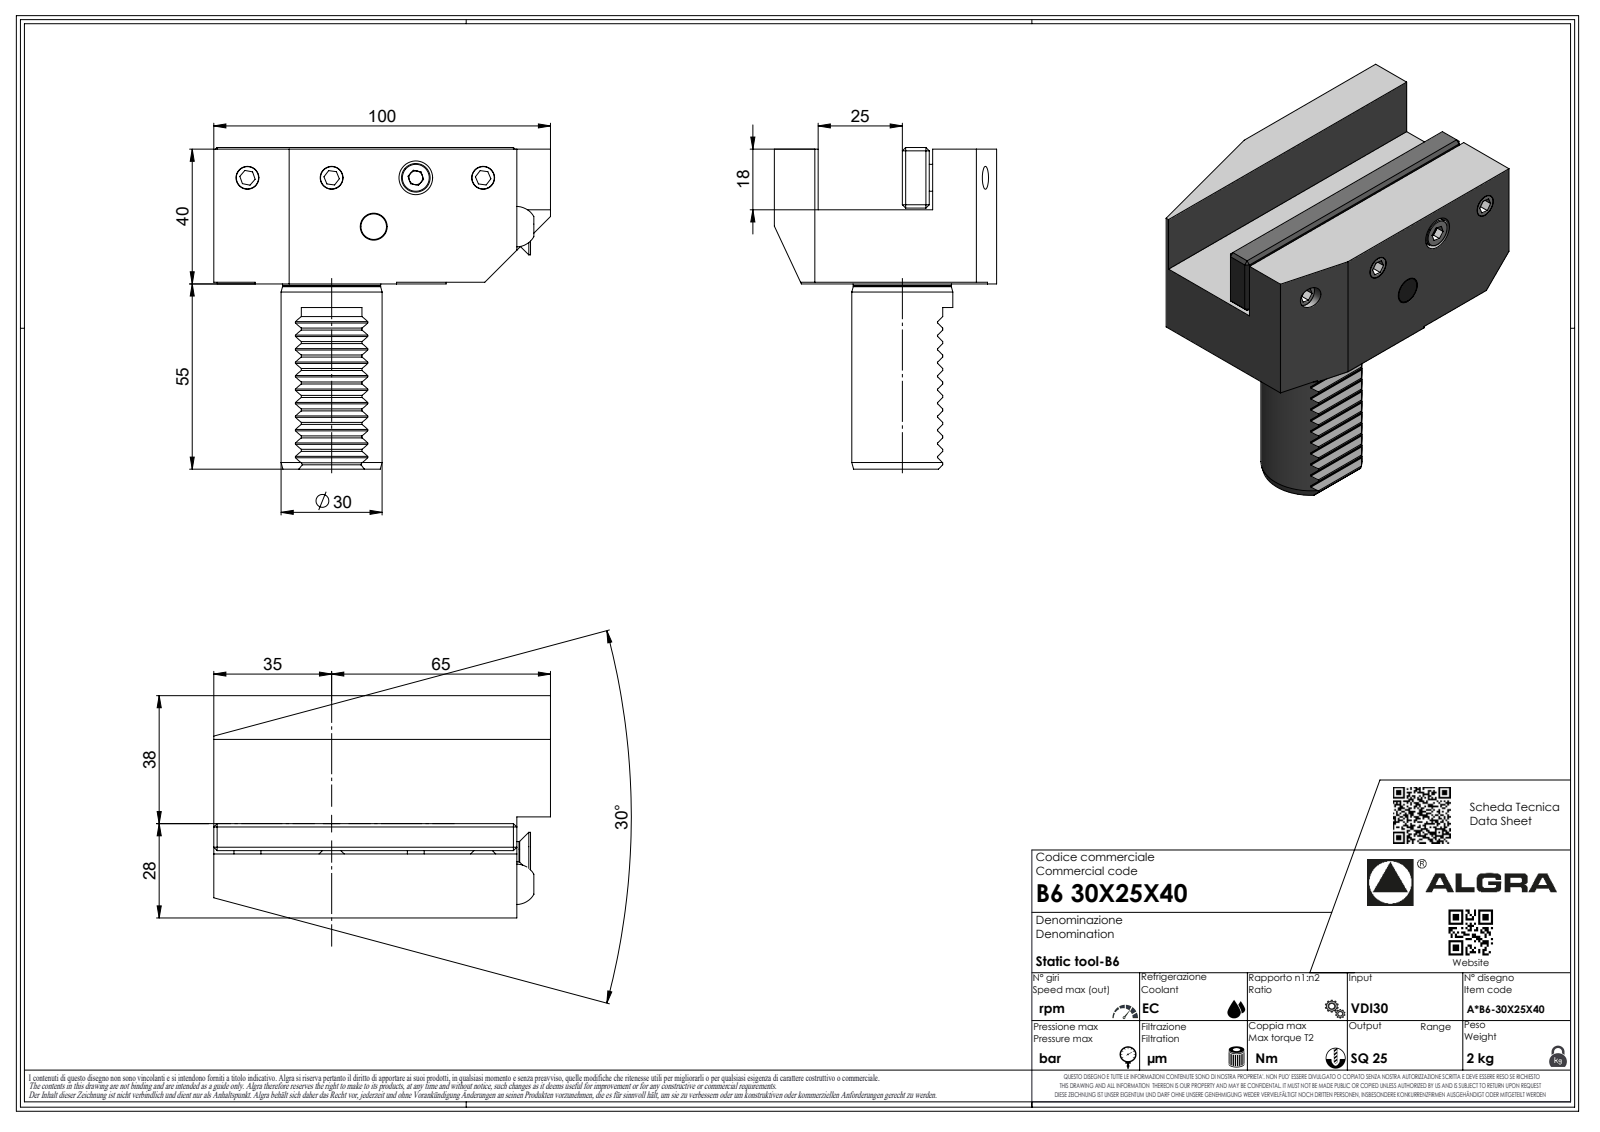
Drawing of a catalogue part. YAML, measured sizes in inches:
part_name: "B630X25X40"
step_written_by: "SolidWorks 2023 (AUTOMOTIVE_DESIGN)"
units: inches
bodies: {solids: 1, faces: 367, planar: 252, cylindrical: 41, other: 74}
overall_size: [3.937, 3.76, 2.598]
volume: 13.24
surface_area: 50.79
round_holes:
  - {diameter: 0.083, count: 1}
round_bosses_or_shafts:
  - {diameter: 1.181, count: 1}
  - {diameter: 1.146, count: 1}
  - {diameter: 0.251, count: 1}
  - {diameter: 0.067, count: 1}
partial_cylinders:
  - {radius: 0.012, count: 11}
  - {radius: 0.013, count: 7}
  - {radius: 0.02, count: 7}
  - {radius: 0.146, count: 7}
  - {radius: 0.008, count: 1}
  - {radius: 1.339, count: 1}
face_to_face_distances: [0.709, 0.866, 1.575, 0.02, 2.087, 0.984, 1.102, 1.555, 0.512, 1.496]
